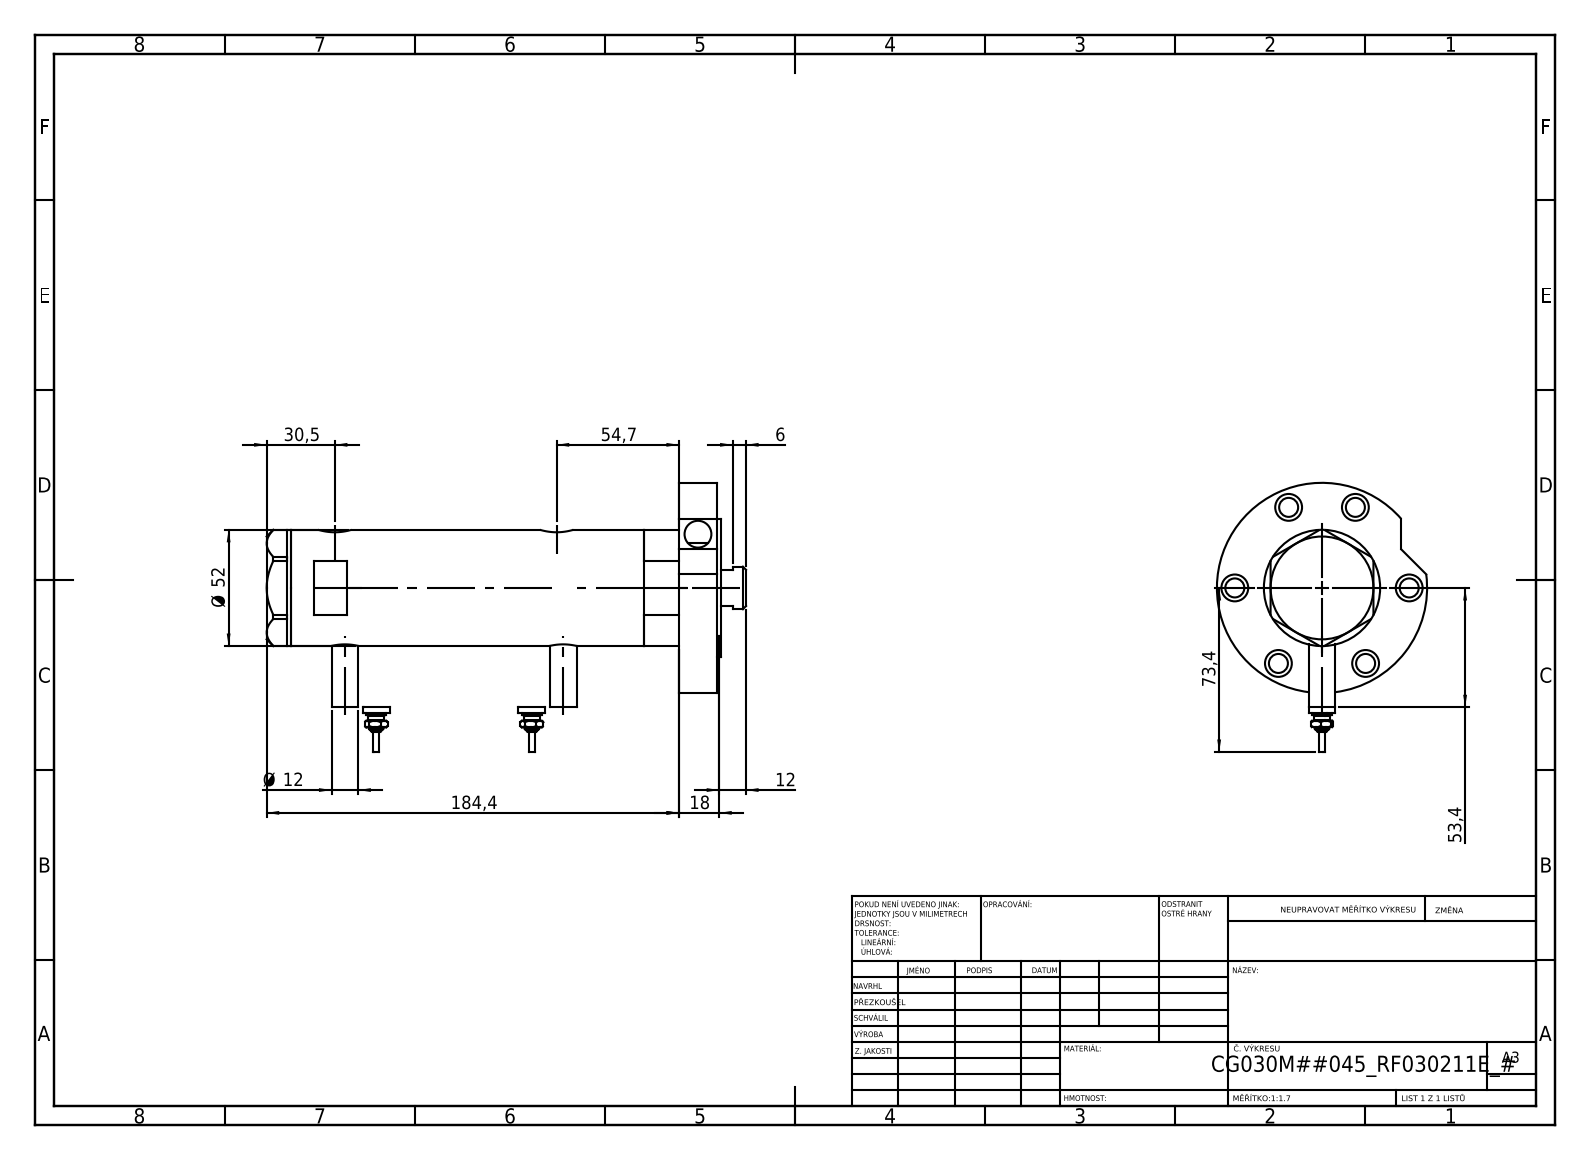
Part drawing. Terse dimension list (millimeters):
name: V270CG_FRONT; V270CG_VC; Switch; V270CG_MIDDLE (+2 more)
written by: SolidWorks 2019 (CONFIG_CONTROL_DESIGN)
unit: mm
bodies: 7 solids, 270 faces (104 planar, 102 cylindrical, 64 other)
size: 214.4 × 120.4 × 94
volume: 480 567 mm³; area: 113 779 mm²
holes: 7× ⌀12, 6× ⌀8.5, 2× ⌀9.73, 2× ⌀12.5, 2× ⌀15, 1× ⌀6.5, 1× ⌀20, 1× ⌀21.5, 1× ⌀30, 1× ⌀33, 1× ⌀40, 1× ⌀44
bosses: 4× ⌀12, 2× ⌀9, 2× ⌀7, 2× ⌀4.5, 2× ⌀2.5, 1× ⌀94, 1× ⌀62, 1× ⌀52
face distances: 17, 173.4, 190.4, 2, 192.4, 121.5, 51.9, 68.9, 11, 203.4
hole spacings: 39, 43.34, 64.85, 67.55, 69.95, 77.83, 2.9, 4.5
